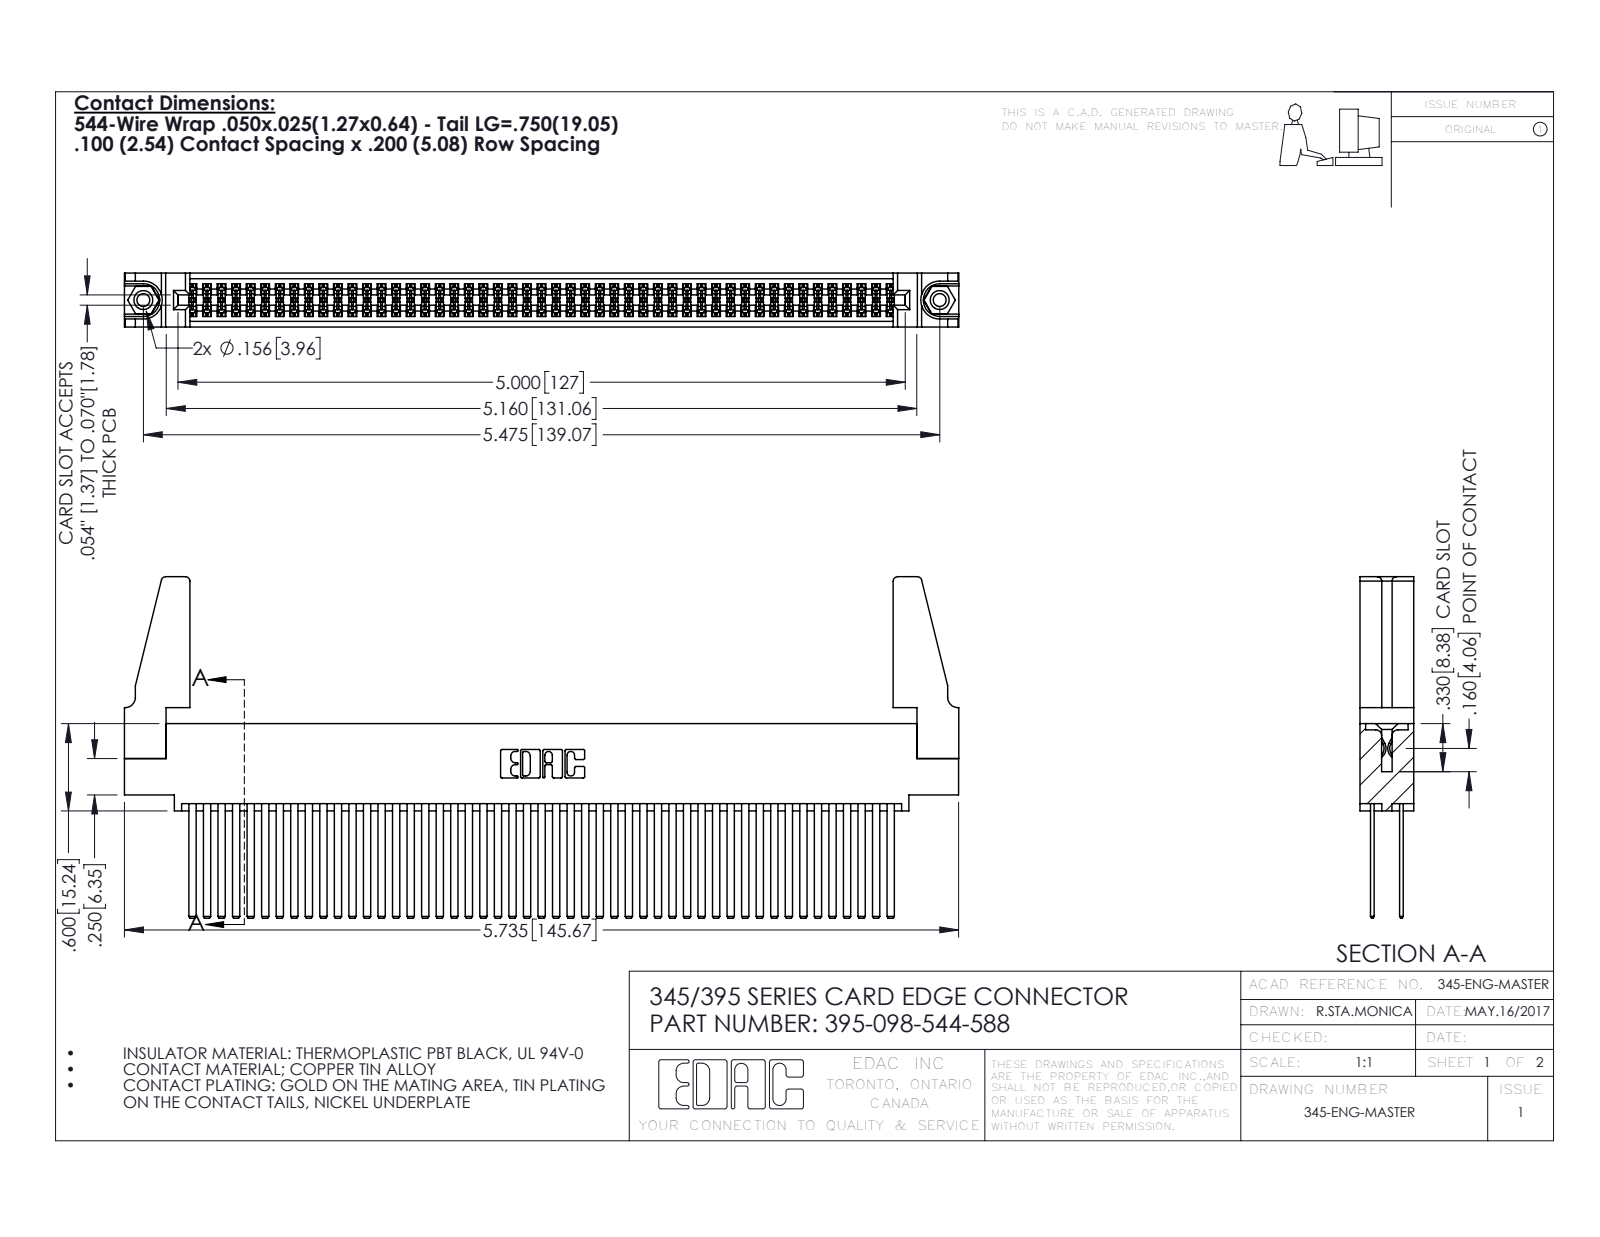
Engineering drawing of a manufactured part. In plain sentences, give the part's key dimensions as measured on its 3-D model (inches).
The part is named "345-220-078_345-220-088; 395-098-544-588; 345-292-001_345-293-144; 345-250-001_345-250-001-102 (+1 more)". Its 3-D file was written by "SolidWorks 2016 (CONFIG_CONTROL_DESIGN)". It is 103 solids with 4566 faces: 2998 planar, 1552 cylindrical and 16 other. Overall it measures 5.736 by 2.347 by 0.37 inches. Its volume is 1.145 cubic inches and its surface area 46.99 square inches. Round holes: 2 of diameter 0.089, 2 of diameter 0.125, 2 of diameter 0.156, 1 of diameter 0.064. Round bosses or shafts: 2 of diameter 0.155. Partial cylindrical surfaces (rounded edges, fillets, slot ends): 147 of radius 0.006, 22 of radius 0.01, 8 of radius 0.03, 6 of radius 0.007, 6 of radius 0.031, 3 of radius 0.026, 2 of radius 0.014, 2 of radius 0.019. The main face-to-face distances are 0.072, 0.298, 0.2, 0.098, 0.272, 0.025, 0.225, 0.37, 0.175, 0.149. The hole center spacings are 0.27, 5.239, 5.475.
